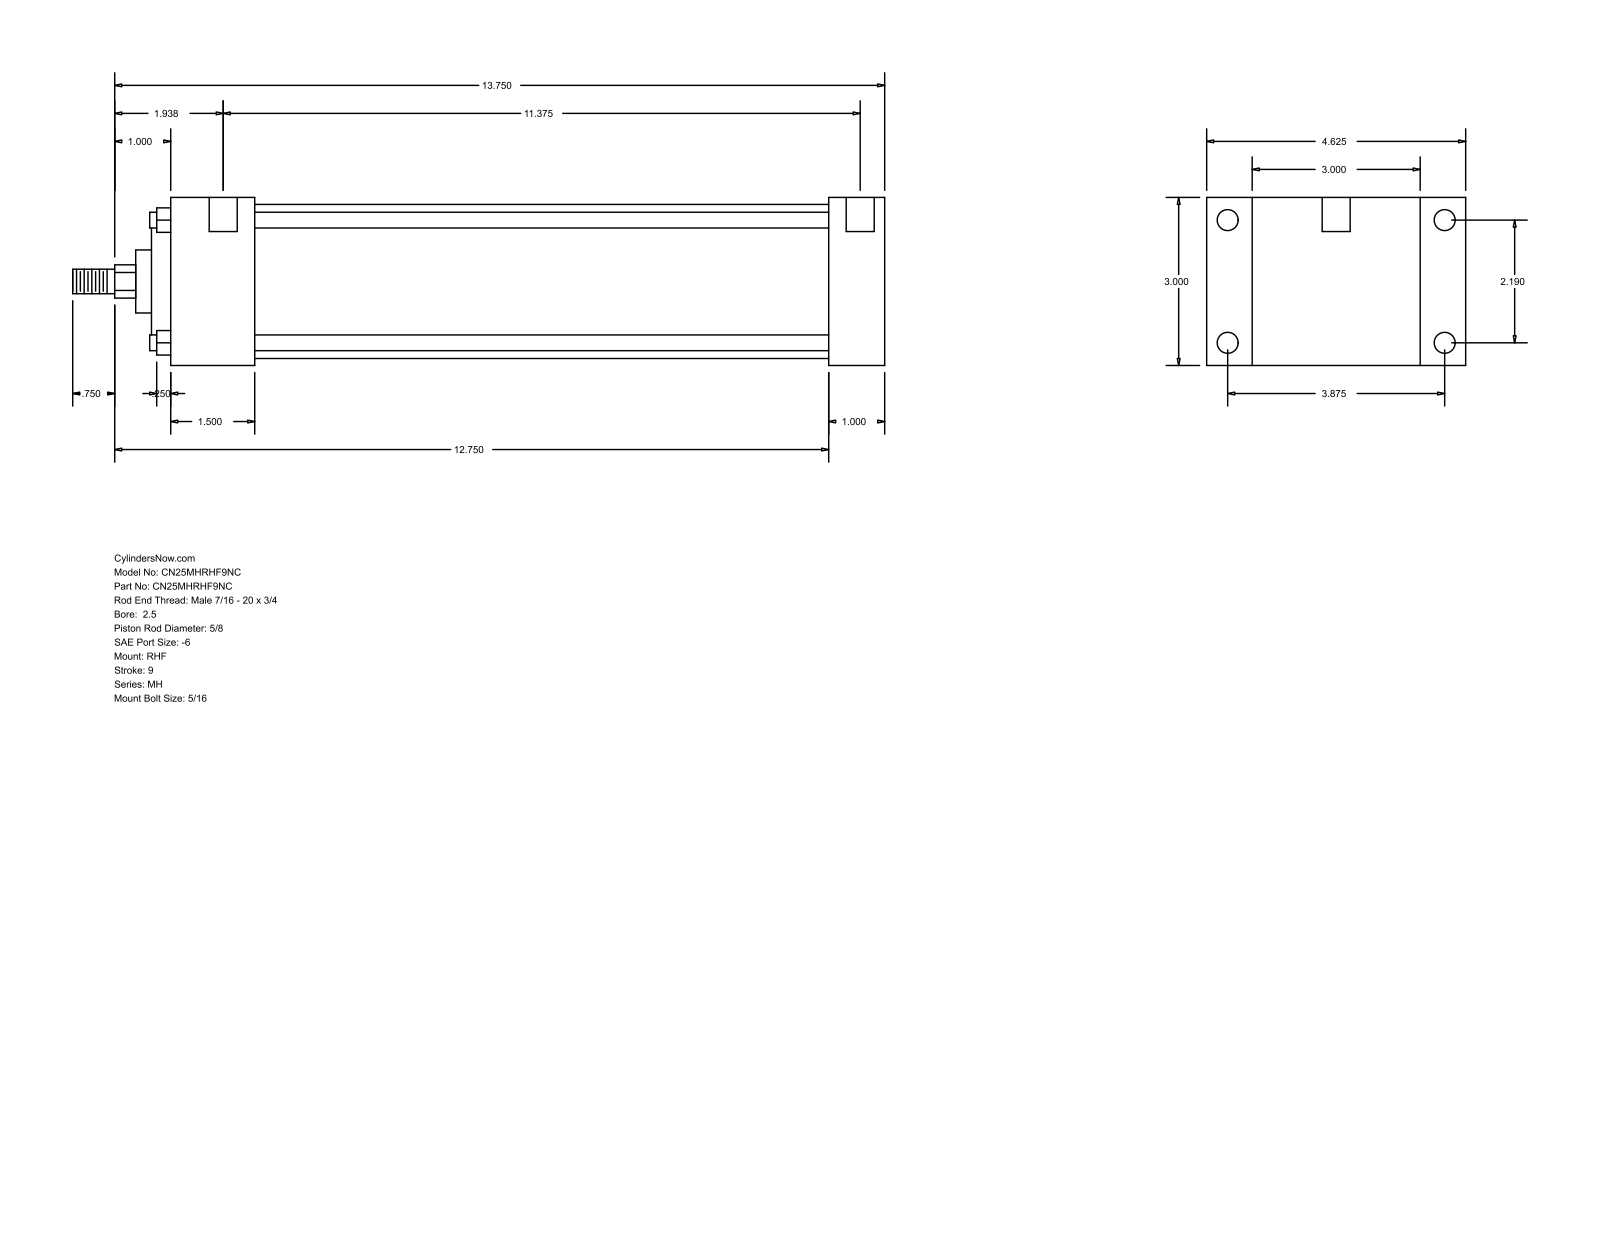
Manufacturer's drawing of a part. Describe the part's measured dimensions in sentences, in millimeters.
The part is named "MH_RHF__0250_0.625". Its 3-D file was written by "GSSL Pune (CONFIG_CONTROL_DESIGN)". It is 0 solids with 90 faces: 61 planar, 29 cylindrical and 0 other. Overall it measures 368.3 by 117.47 by 76.2 millimeters. Round holes: 4 of diameter 5.56, 4 of diameter 9.53, 2 of diameter 12.7. Round bosses or shafts: 4 of diameter 7.14, 1 of diameter 69.85, 1 of diameter 55.55, 1 of diameter 28.57, 1 of diameter 15.88, 1 of diameter 11.11. Partial cylindrical surfaces (rounded edges, fillets, slot ends): 1 of radius 7.54. The main face-to-face distances are 76.2, 25.4, 20.64, 96.84, 323.85, 298.45, 38.1, 117.48, 260.35, 285.75. The hole center spacings are 55.62, 98.42, 113.05, 296.86, 3.17, 4.76, 288.93, 292.1.
